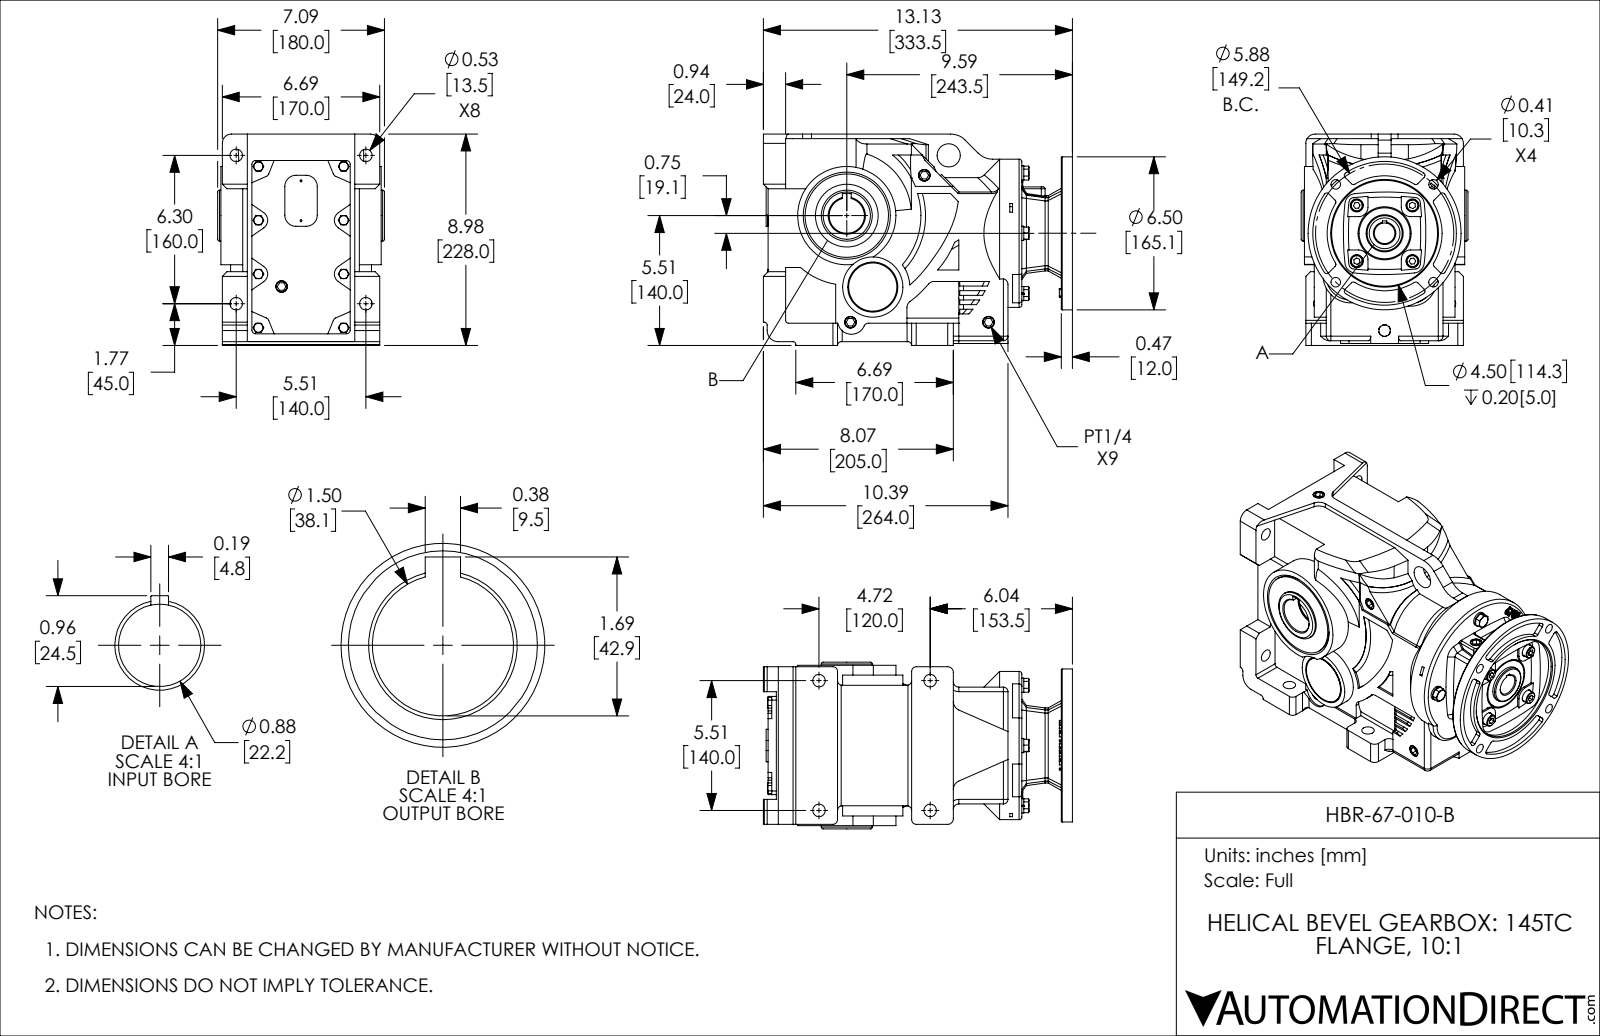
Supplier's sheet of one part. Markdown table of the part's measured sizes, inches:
| quantity | value |
| --- | --- |
| part name | HBR-67-010-B |
| STEP written by | SolidWorks 2018 (AUTOMOTIVE_DESIGN) |
| units | inches |
| bodies | 1 solid, 1131 faces (598 planar, 268 cylindrical, 265 other) |
| overall size | 13.13 × 8.976 × 7.087 |
| volume | 482.9 in³ |
| surface area | 639 in² |
| round holes (diameter × count) | 0.531 × 8, 0.323 × 4, 0.354 × 4, 0.406 × 4, 0.551 × 4, 0.079 × 2, 0.875 × 1, 0.984 × 1, 1.102 × 1, 1.5 × 1, 1.575 × 1, 4.5 × 1 |
| round bosses / shafts (diameter × count) | 0.606 × 4, 0.512 × 4, 0.315 × 4, 2.165 × 2, 6.5 × 1, 6.299 × 1, 4.173 × 1, 3.543 × 1 |
| partial cylindrical surfaces (radius × count) | 0.197 × 20, 0.118 × 19, 0.394 × 15, 0.157 × 12, 0.079 × 7, 0.472 × 5, 0.236 × 4, 11.811 × 4 |
| main face-to-face distances | 0.197, 0.079, 0.945, 0.276, 0.059, 8.78, 4.961, 0.157, 0.118, 1.949 |
| hole center spacings | 2.132, 3.925, 1.264, 1.673, 1.815, 2.559, 2.937, 3.38 |
